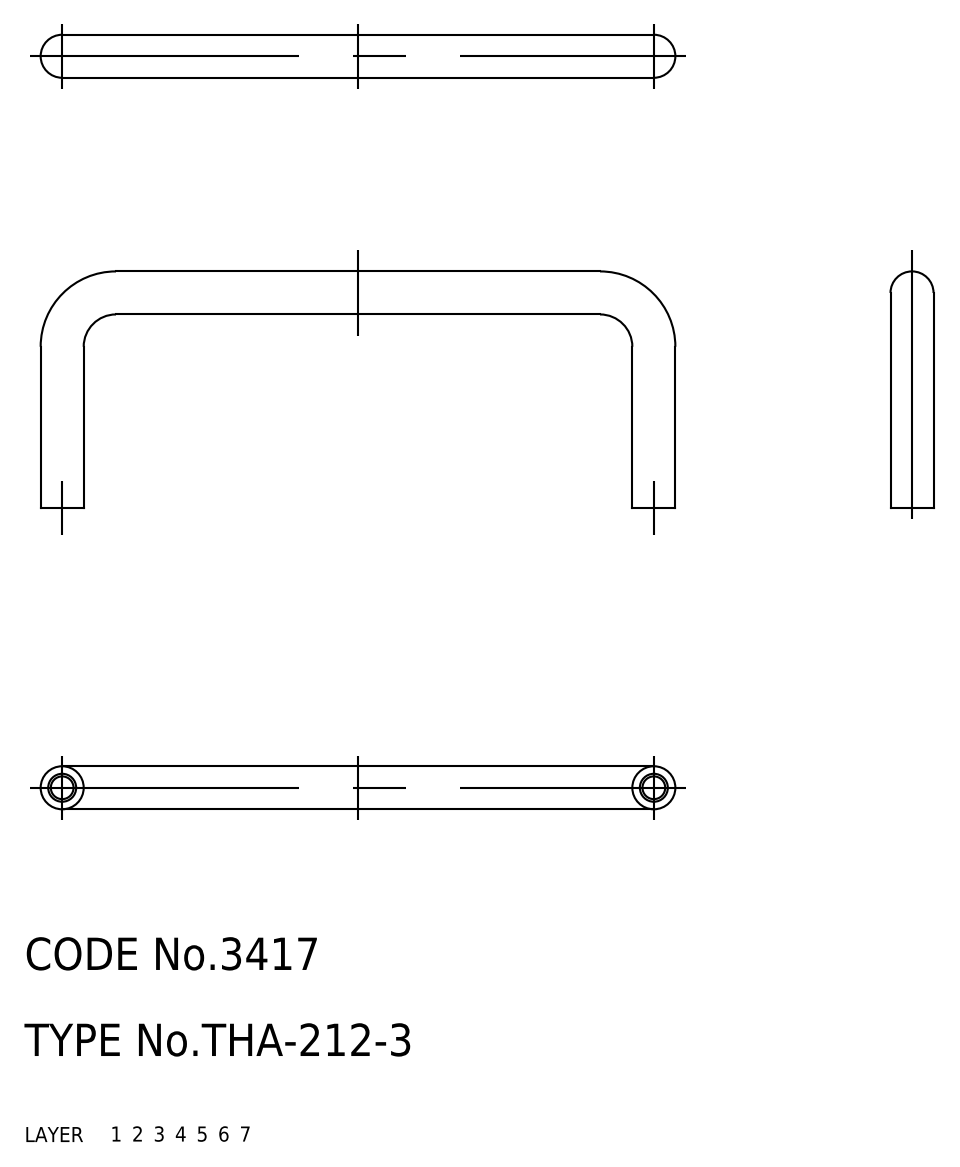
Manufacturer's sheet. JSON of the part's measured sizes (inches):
{"part_name": "pull", "step_written_by": "CADfix (AUTOMOTIVE_DESIGN)", "units": "inches", "bodies": {"solids": 1, "faces": 18, "planar": 0, "cylindrical": 0, "other": 18}, "overall_size": [2.323, 0.866, 0.157], "volume_in3": 0.064, "surface_area_in2": 2.06}
